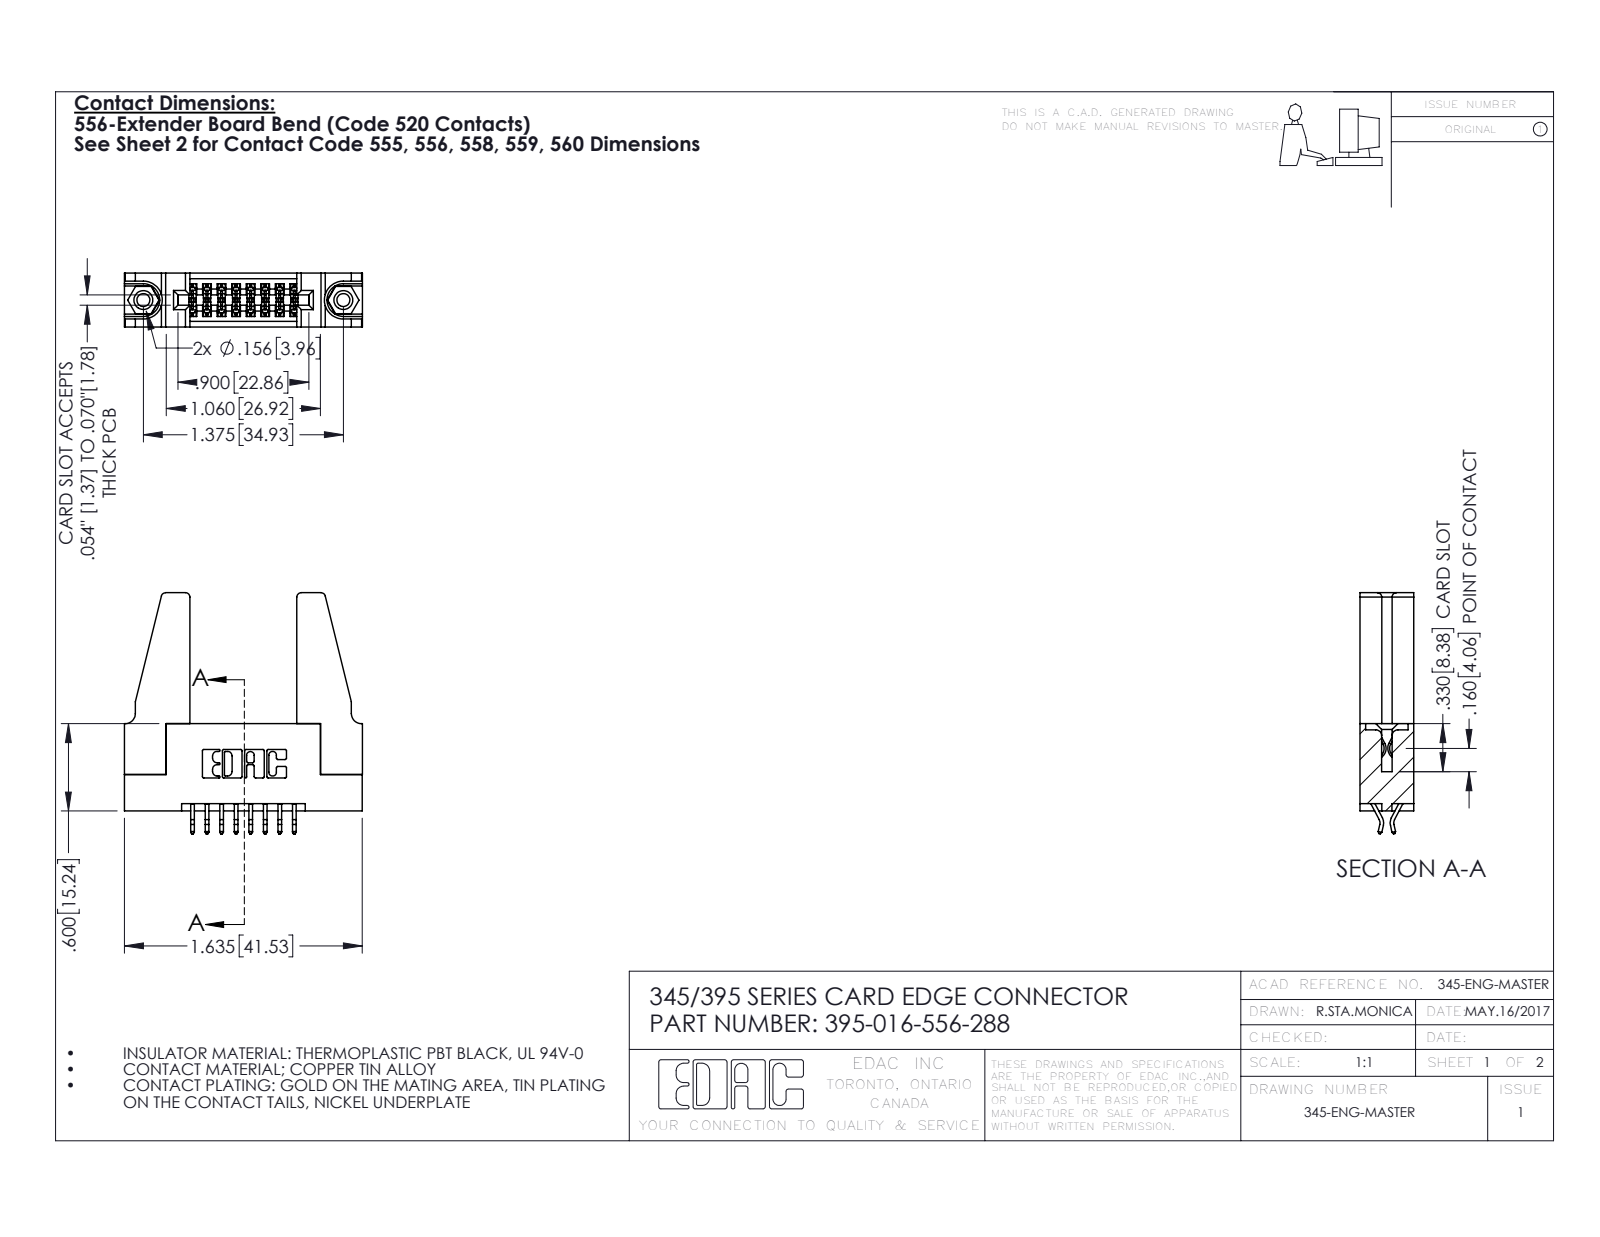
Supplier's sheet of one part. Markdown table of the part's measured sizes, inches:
| quantity | value |
| --- | --- |
| part name | 395-016-556-288; 345-292-001_556 Tail; 345-250-001_345-250-001-102; 345-220-078_345-220-088 (+1 more) |
| STEP written by | SolidWorks 2016 (CONFIG_CONTROL_DESIGN) |
| units | inches |
| bodies | 21 solids, 1146 faces (744 planar, 386 cylindrical, 16 other) |
| overall size | 1.657 × 1.636 × 0.37 |
| volume | 0.426 in³ |
| surface area | 12.32 in² |
| round holes (diameter × count) | 0.089 × 2, 0.125 × 2, 0.156 × 2, 0.064 × 1 |
| round bosses / shafts (diameter × count) | 0.155 × 2 |
| partial cylindrical surfaces (radius × count) | 0.006 × 24, 0.01 × 22, 0.03 × 8, 0.007 × 6, 0.031 × 6, 0.026 × 3, 0.01 × 2, 0.014 × 2 |
| main face-to-face distances | 0.37, 0.072, 0.298, 0.2, 0.025, 0.225, 0.098, 0.272, 0.15, 0.148 |
| hole center spacings | 0.27, 1.144, 1.375 |
